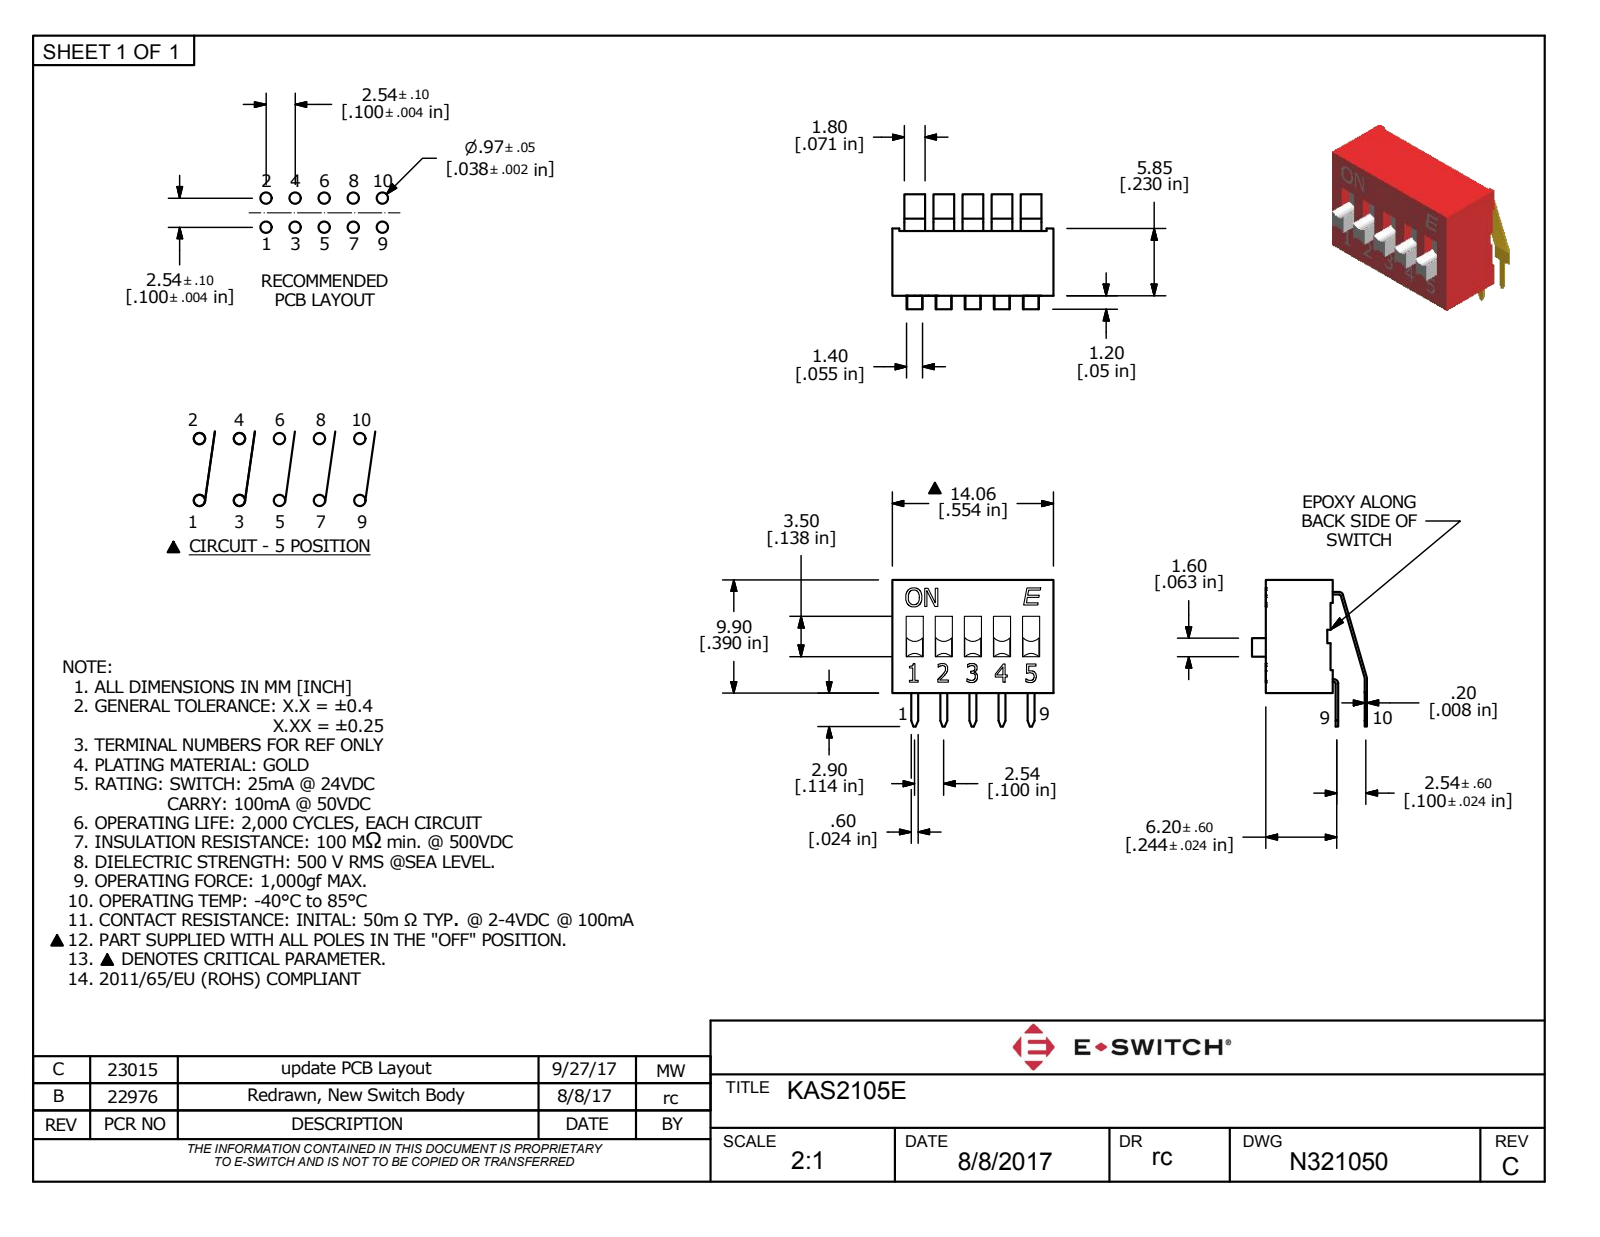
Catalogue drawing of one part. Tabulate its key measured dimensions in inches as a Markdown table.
| quantity | value |
| --- | --- |
| part name | P:\\\\E-Switch Secure\\\\3D_MODELS_STP_FORMAT\\\\KAS2105E.stp |
| STEP written by | ACIS (CONFIG_CONTROL_DESIGN) |
| units | inches |
| bodies | 1 solid, 301 faces (281 planar, 20 cylindrical, 0 other) |
| overall size | 0.554 × 0.504 × 0.386 |
| volume | 0.043 in³ |
| surface area | 1.413 in² |
| partial cylindrical surfaces (radius × count) | 0.035 × 10, 0.01 × 1, 0.016 × 1 |
| main face-to-face distances | 0.194, 0.39, 0.1, 0.554, 0.159, 0.2, 0.024, 0.02, 0.214, 0.3 |
